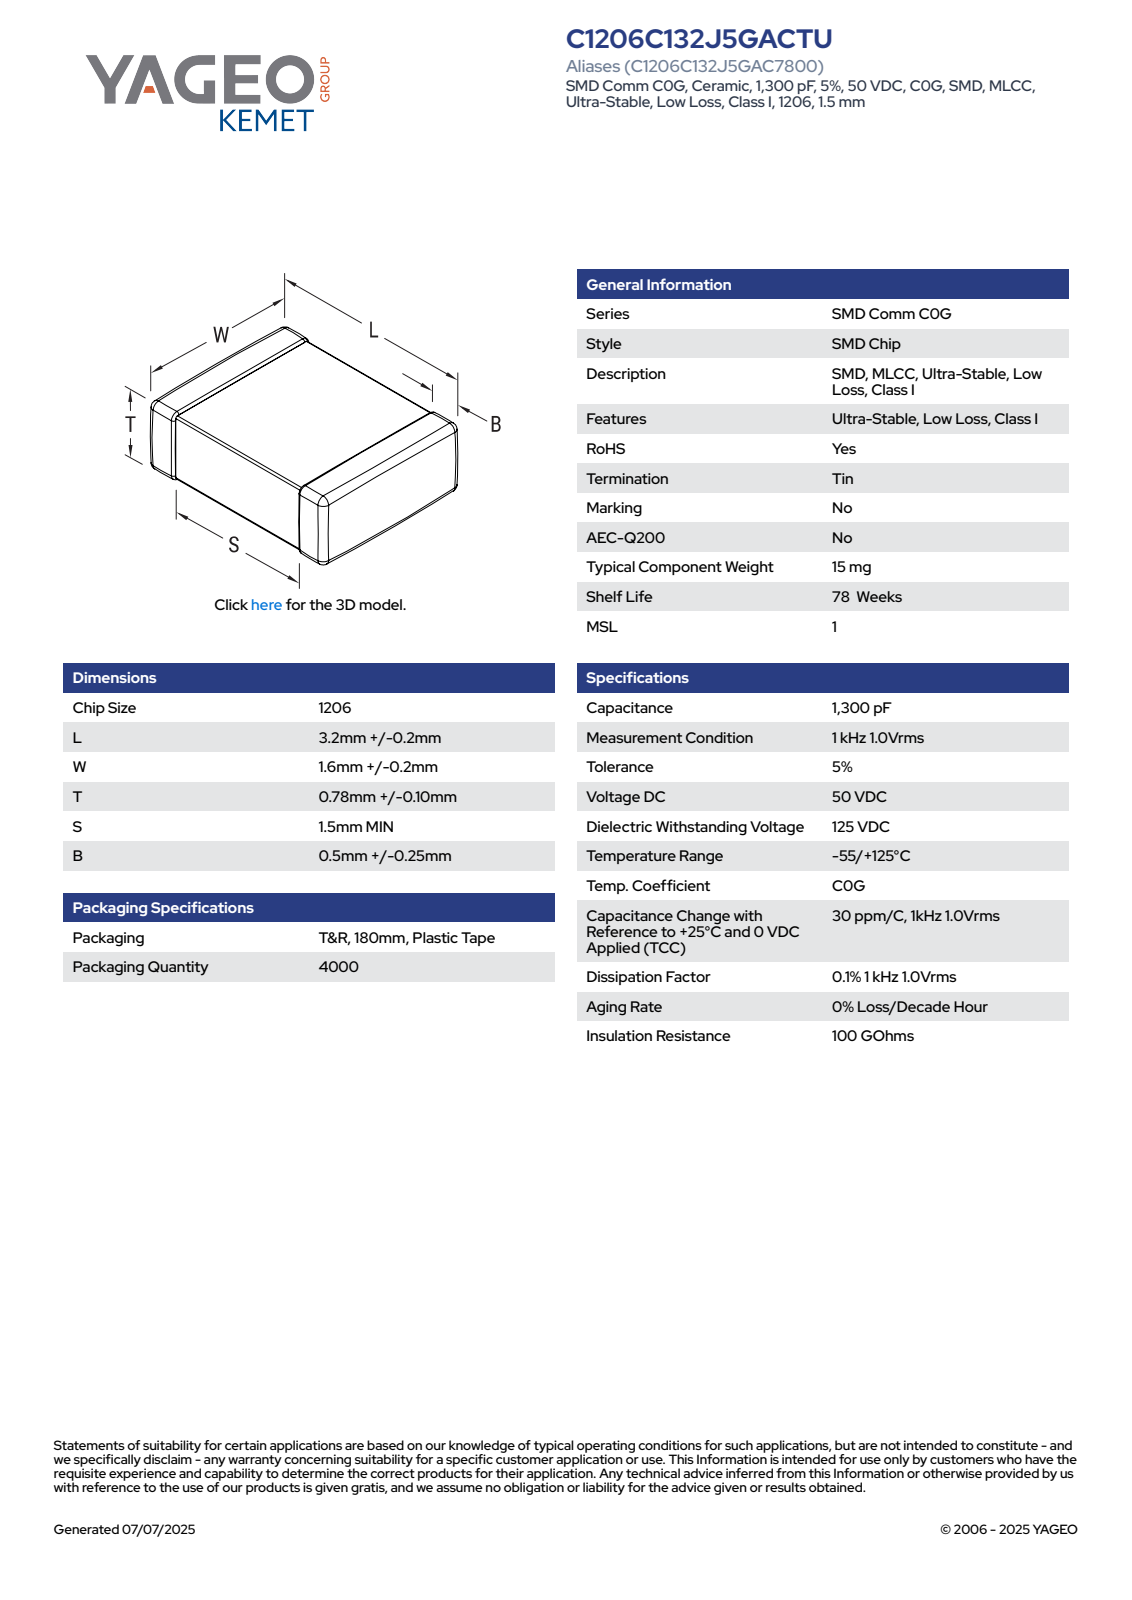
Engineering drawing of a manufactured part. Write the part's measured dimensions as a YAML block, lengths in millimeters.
part_name: "CCS_CCSTDNOS_1206_L3.4W1.8T0.88B0.75"
step_written_by: "SolidWorks 2014 (AUTOMOTIVE_DESIGN)"
units: millimeters
bodies: {solids: 4, faces: 125, planar: 71, cylindrical: 38, other: 16}
overall_size: [3.4, 1.8, 0.88]
volume: 5
surface_area: 21
face_to_face_distances: [0.84, 0.8, 0.88, 1.76, 3.4, 1.72, 1.8, 0.81, 0.85, 0.99]
